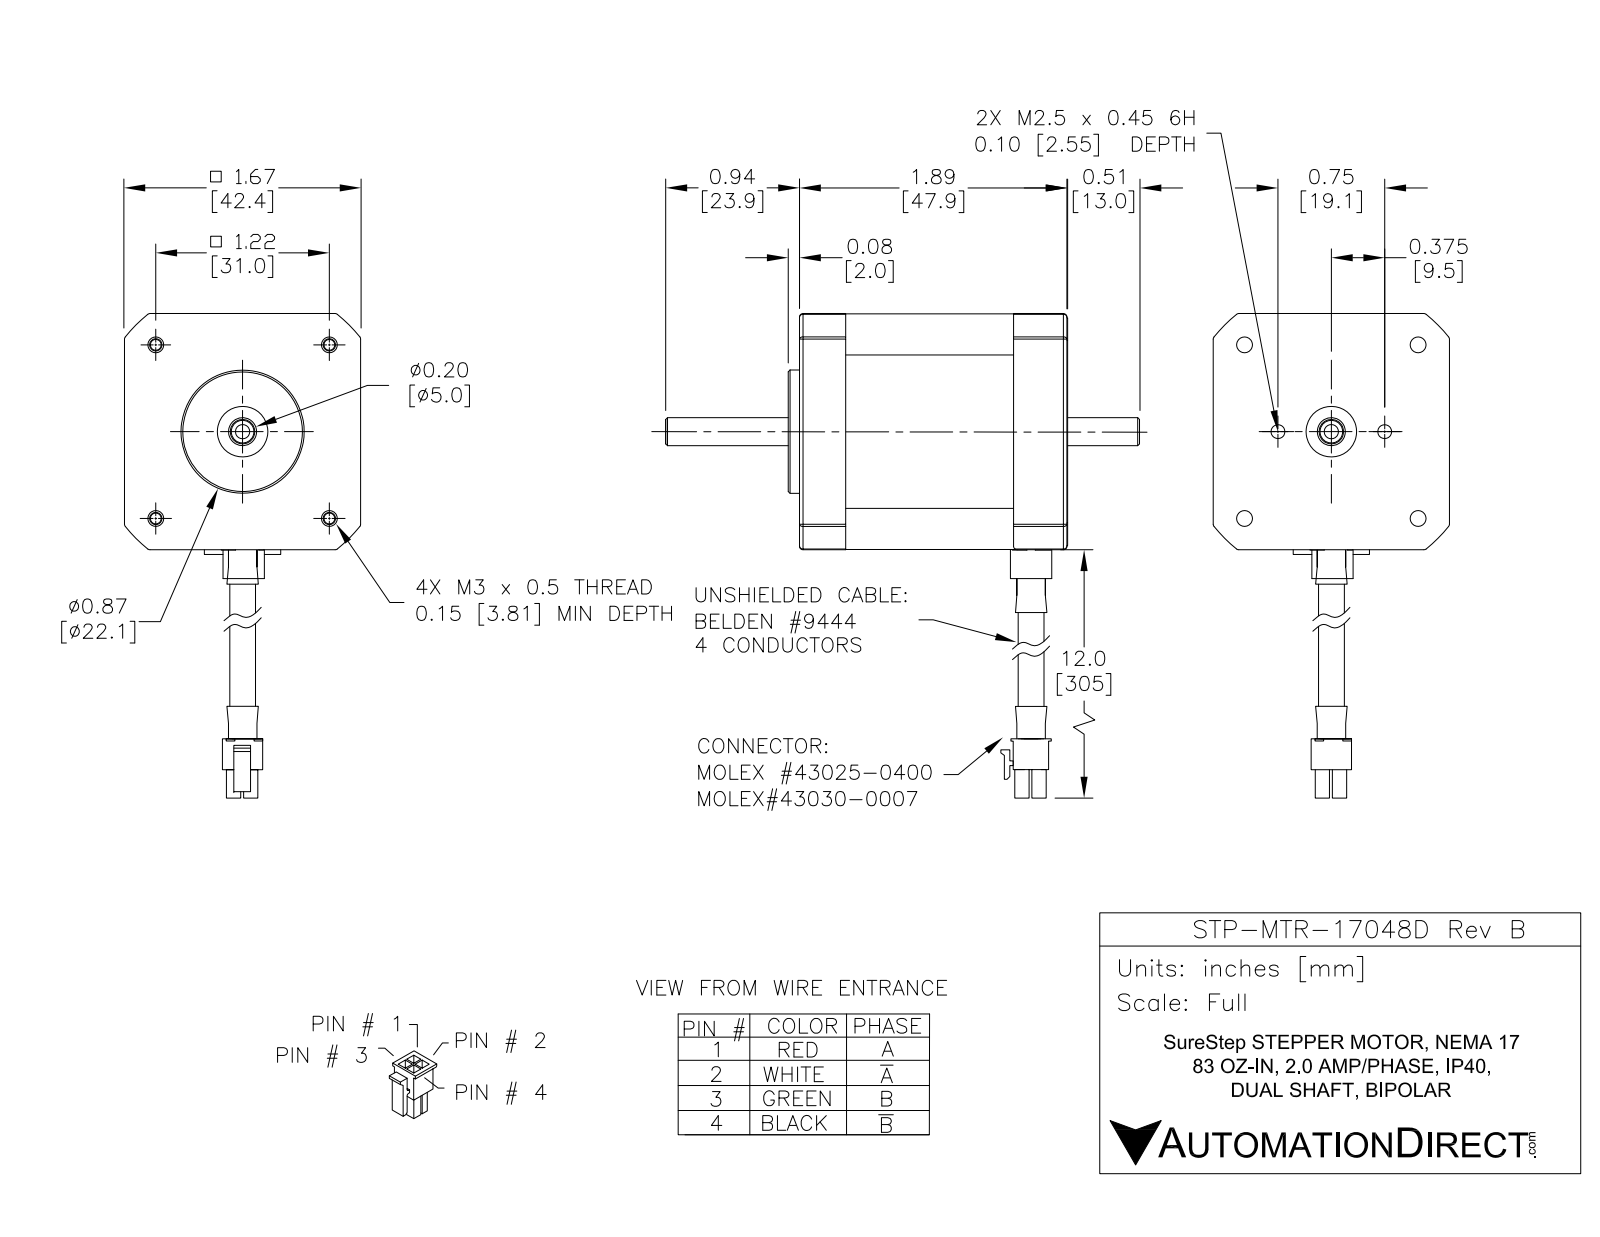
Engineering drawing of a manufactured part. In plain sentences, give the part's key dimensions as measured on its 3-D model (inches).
The part is named "STP-MTR-17048E". Its 3-D file was written by "SolidWorks 2017 (AUTOMOTIVE_DESIGN)". It is 8 solids with 425 faces: 257 planar, 110 cylindrical and 58 other. Overall it measures 13.976 by 3.33 by 1.66 inches. Its volume is 5.507 cubic inches and its surface area 32.29 square inches. Round holes: 4 of diameter 0.086, 4 of diameter 0.15, 2 of diameter 0.079, 1 of diameter 0.05, 1 of diameter 0.25, 1 of diameter 0.355. Round bosses or shafts: 4 of diameter 0.13, 1 of diameter 0.866, 1 of diameter 0.29, 1 of diameter 0.217, 1 of diameter 0.197. Partial cylindrical surfaces (rounded edges, fillets, slot ends): 17 of radius 0.025, 3 of radius 0.012, 1 of radius 0.006, 1 of radius 0.147, 1 of radius 0.986, 1 of radius 0.988, 1 of radius 1.025, 1 of radius 1.06. The main face-to-face distances are 1.658, 1.656, 1.885, 1.66, 0.118, 1.964, 0.079, 0.098, 0.089, 0.145. The hole center spacings are 1.159, 1.22, 0.863, 0.654, 0.654, 1.726, 0.375, 0.375.
